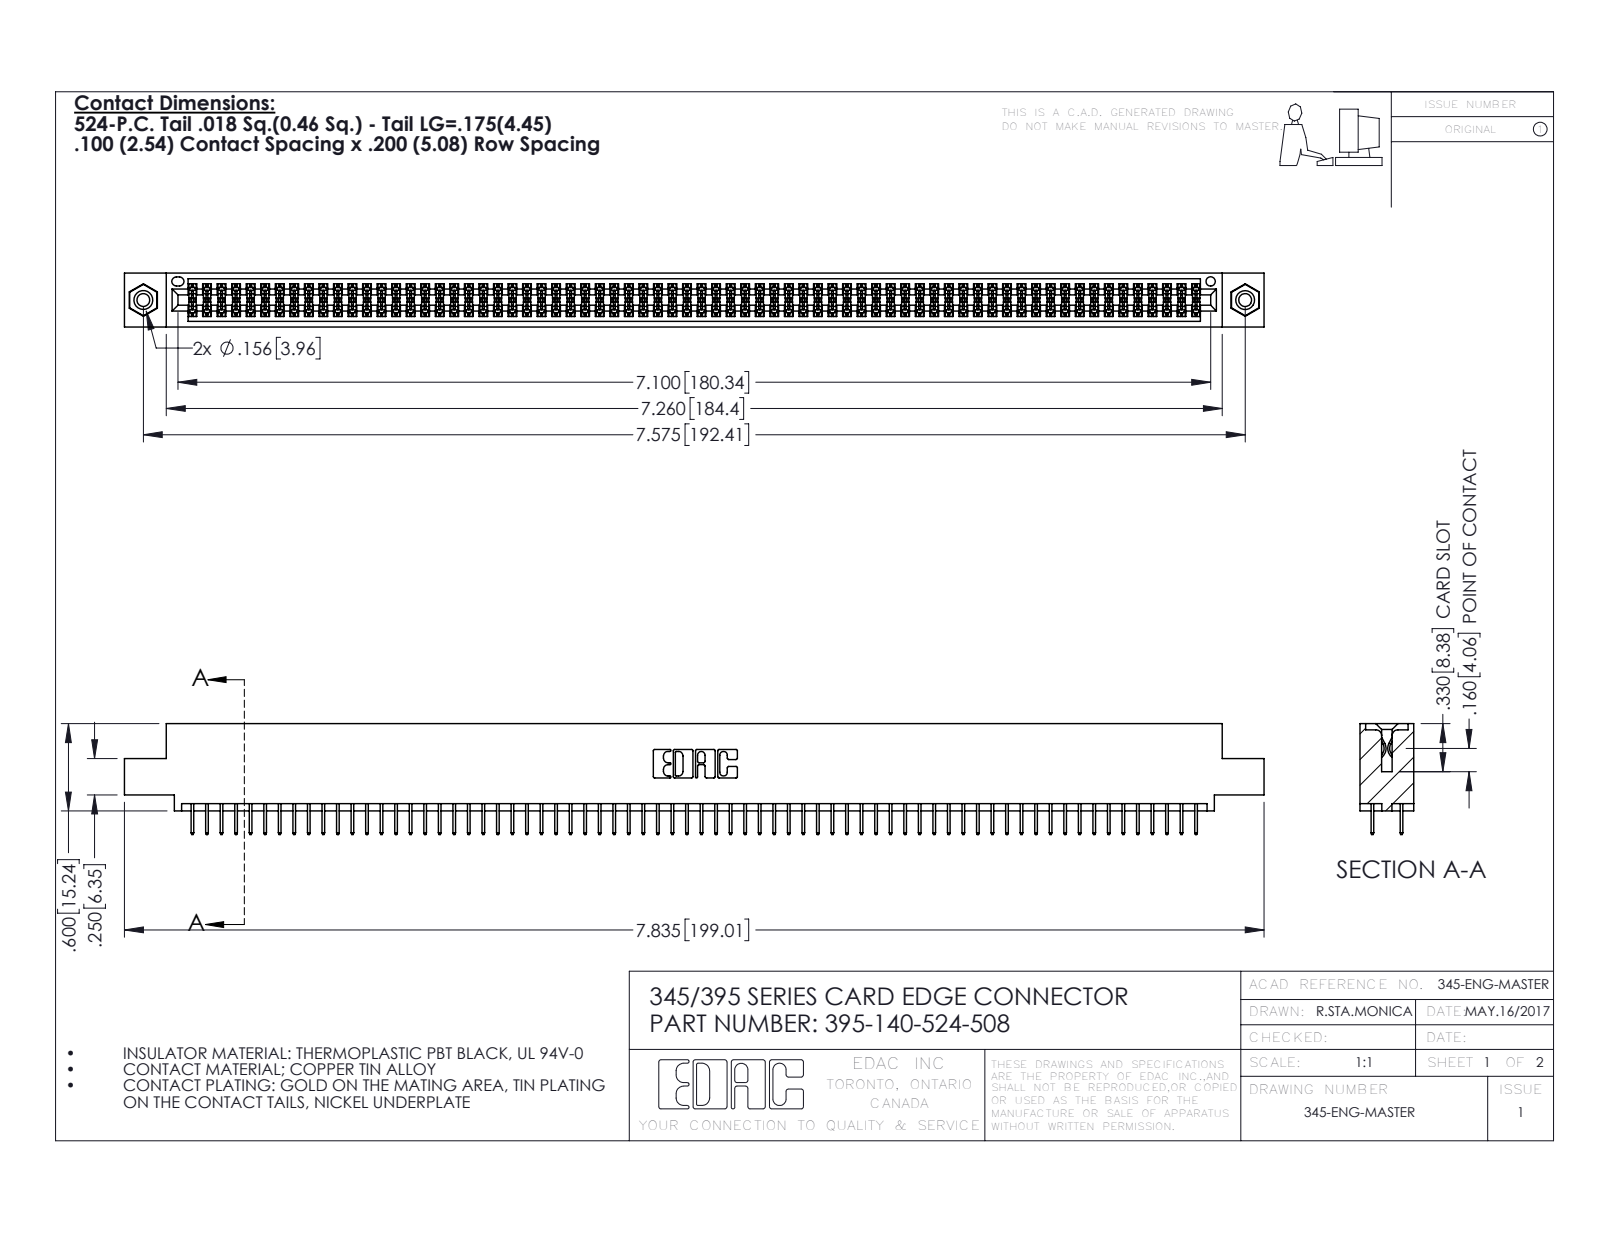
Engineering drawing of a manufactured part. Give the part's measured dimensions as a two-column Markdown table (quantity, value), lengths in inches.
| quantity | value |
| --- | --- |
| part name | 395-140-524-508; 345-292-001_345-293-124; 345 Part_0.110 Offset - 0.156 Dia-TI; 345-250-001_345-250-003-102 |
| STEP written by | SolidWorks 2016 (CONFIG_CONTROL_DESIGN) |
| units | inches |
| bodies | 143 solids, 7750 faces (5576 planar, 2158 cylindrical, 16 other) |
| overall size | 7.835 × 0.762 × 0.37 |
| volume | 1.178 in³ |
| surface area | 44.36 in² |
| round holes (diameter × count) | 0.089 × 2, 0.125 × 2, 0.156 × 2, 0.064 × 1 |
| round bosses / shafts (diameter × count) | 0.155 × 2 |
| partial cylindrical surfaces (radius × count) | 0.006 × 210, 0.01 × 22, 0.007 × 6, 0.031 × 6, 0.026 × 3, 0.014 × 2, 0.019 × 2, 0.022 × 2 |
| main face-to-face distances | 0.072, 0.298, 0.2, 0.37, 0.098, 0.272, 0.025, 0.225, 0.072, 0.175 |
| hole center spacings | 0.27, 7.339, 7.575 |
